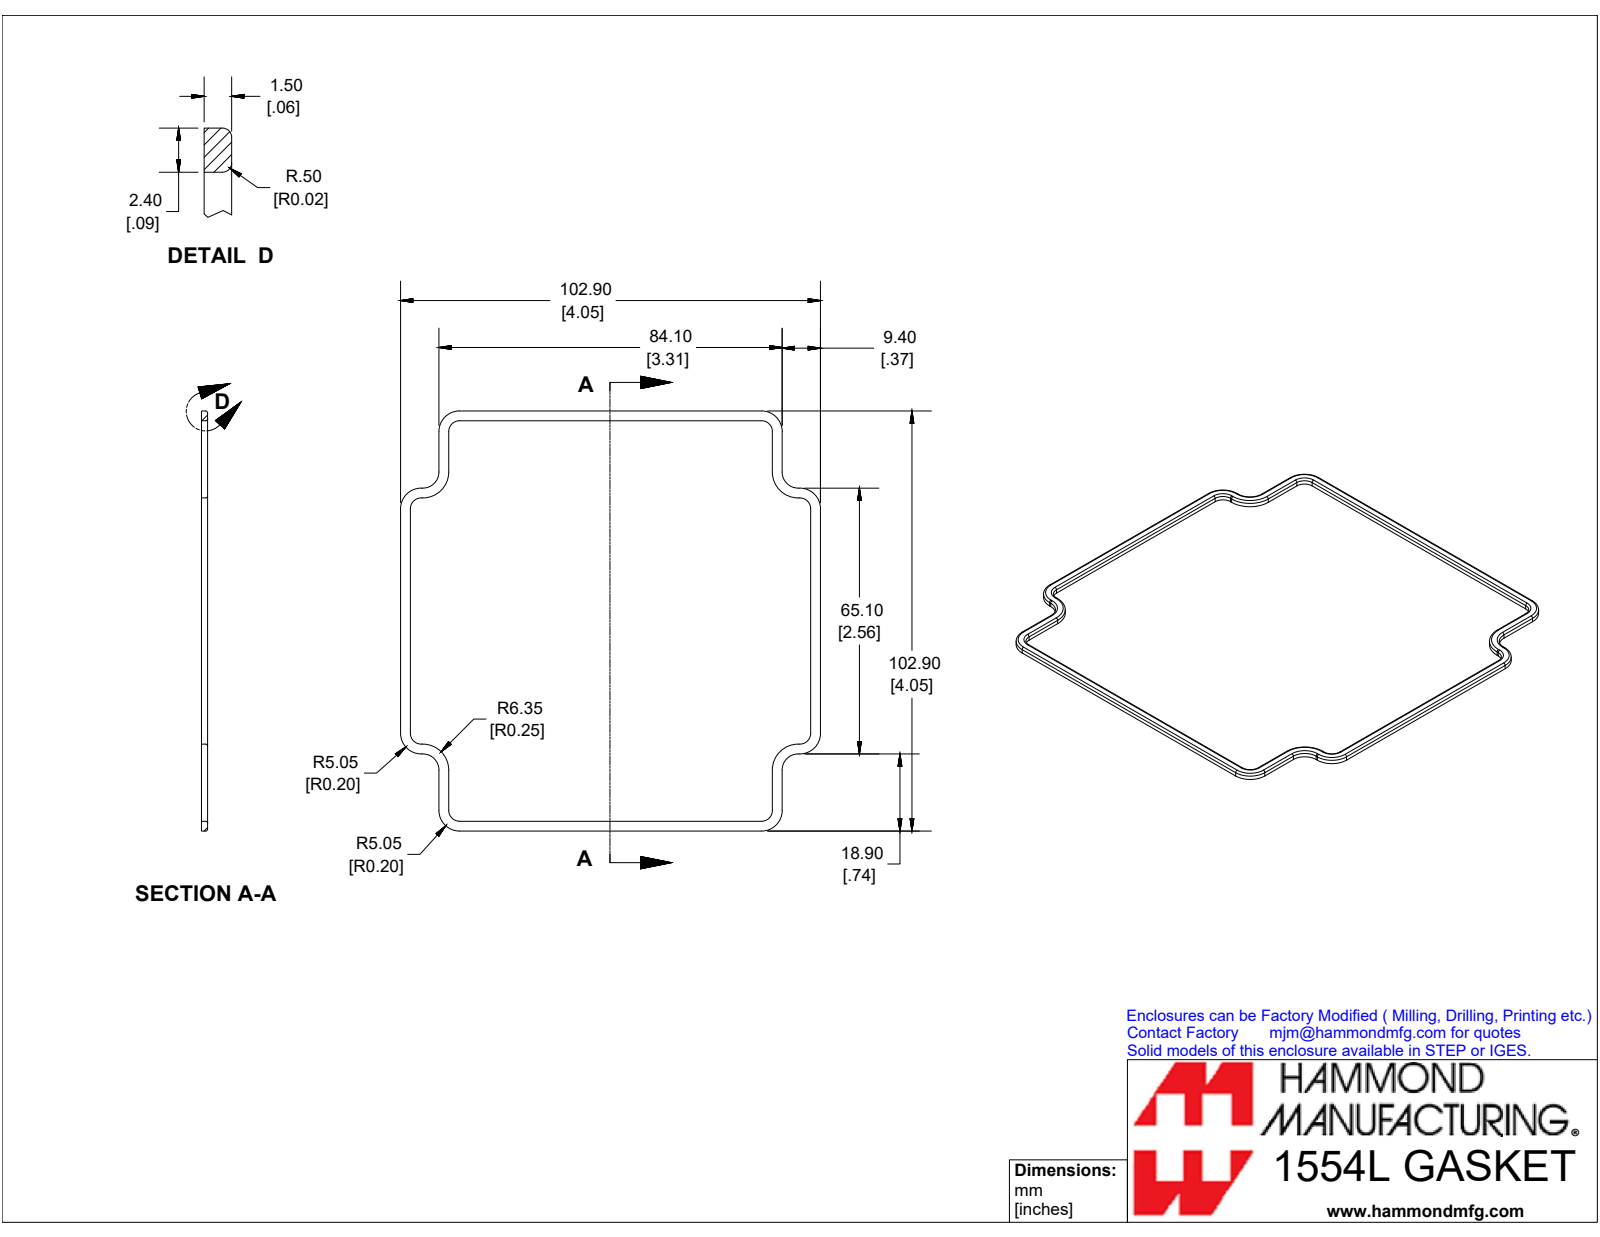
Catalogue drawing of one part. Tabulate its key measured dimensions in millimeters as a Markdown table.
| quantity | value |
| --- | --- |
| part name | 1554LGASKET |
| STEP written by | SolidWorks 2019 (CONFIG_CONTROL_DESIGN) |
| units | millimeters |
| bodies | 1 solid, 98 faces (26 planar, 48 cylindrical, 24 other) |
| overall size | 102.9 × 102.9 × 1.5 |
| volume | 1 300 mm³ |
| surface area | 2 801 mm² |
| partial cylindrical surfaces (radius × count) | 0.5 × 16, 2.6 × 8, 5.1 × 8, 4 × 4, 6.4 × 4 |
| main face-to-face distances | 1.5, 2.4, 100.5, 102.9, 98.1, 9.4, 91.1, 93.5, 7, 11.8 |
